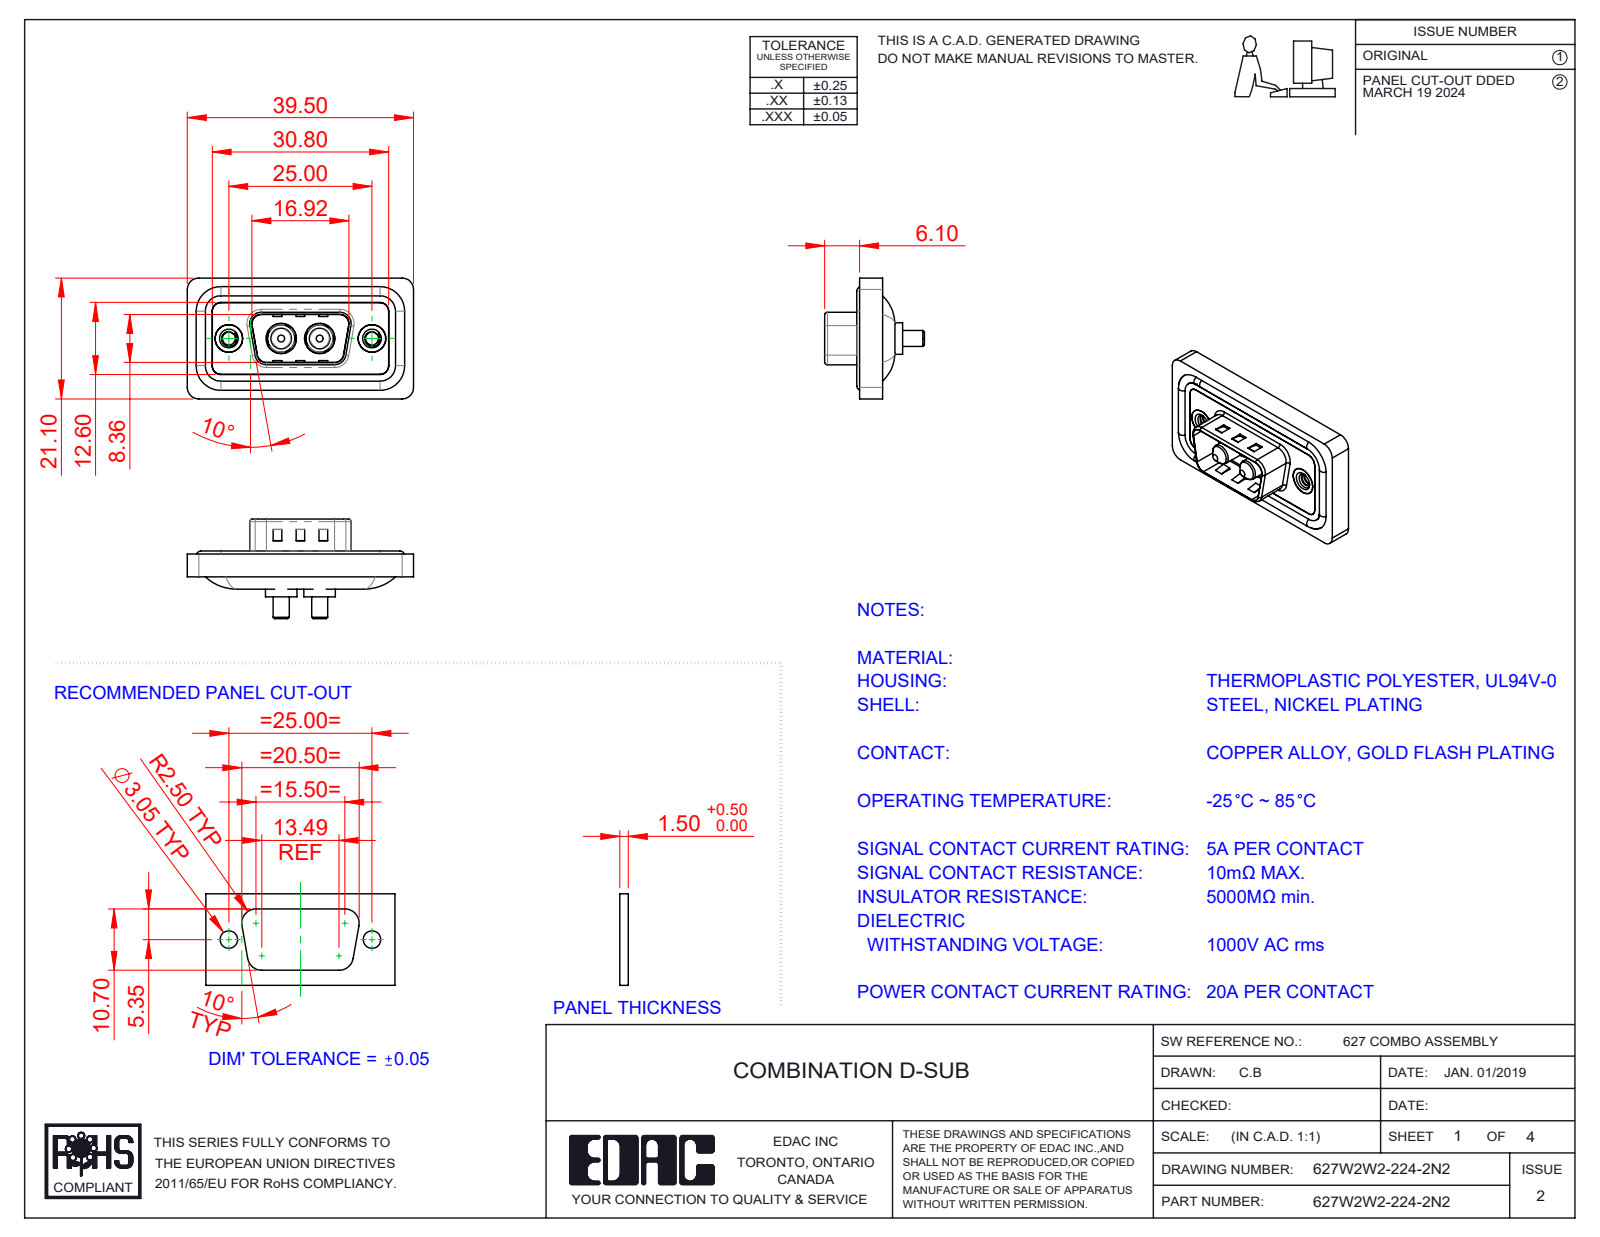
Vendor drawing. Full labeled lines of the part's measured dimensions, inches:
Part name (STEP PRODUCT): 627Combo Threaded Rivet_2; 627Combo Housing_2W2; 627W2W2-224-2N2; 627Combo Shell Front_09 Contacts (+3 more)
STEP written by: SolidWorks 2023 (CONFIG_CONTROL_DESIGN)
Units: inches
Bodies: 11 solids, 489 faces (165 planar, 218 cylindrical, 106 other)
Overall size (bounding box): 1.555 × 0.831 × 0.685
Volume: 0.272 in³ · Surface area: 10.83 in²
Round holes (diameter × count): ⌀0.089 ×2, ⌀0.157 ×2, ⌀0.189 ×2, ⌀0.191 ×2, ⌀0.197 ×2, ⌀0.209 ×2
Round bosses / shafts (diameter × count): ⌀0.063 ×4, ⌀0.217 ×2, ⌀0.205 ×2, ⌀0.193 ×2, ⌀0.187 ×2, ⌀0.148 ×2, ⌀0.142 ×2, ⌀0.11 ×2
Partial cylindrical surfaces — rounded edges, fillets, slot ends (radius × count): R0.059 ×22, R0.079 ×18, R0.02 ×8, R0.063 ×8, R0.01 ×4, R0.024 ×4, R0.026 ×4, R0.035 ×4
Main face-to-face distances: 0.016, 0.043, 0.114, 0.122, 0.02, 0.063, 0.059, 0.157, 0.098, 0.028
Hole centre spacings: 0.36, 0.624, 0.265, 0.984
